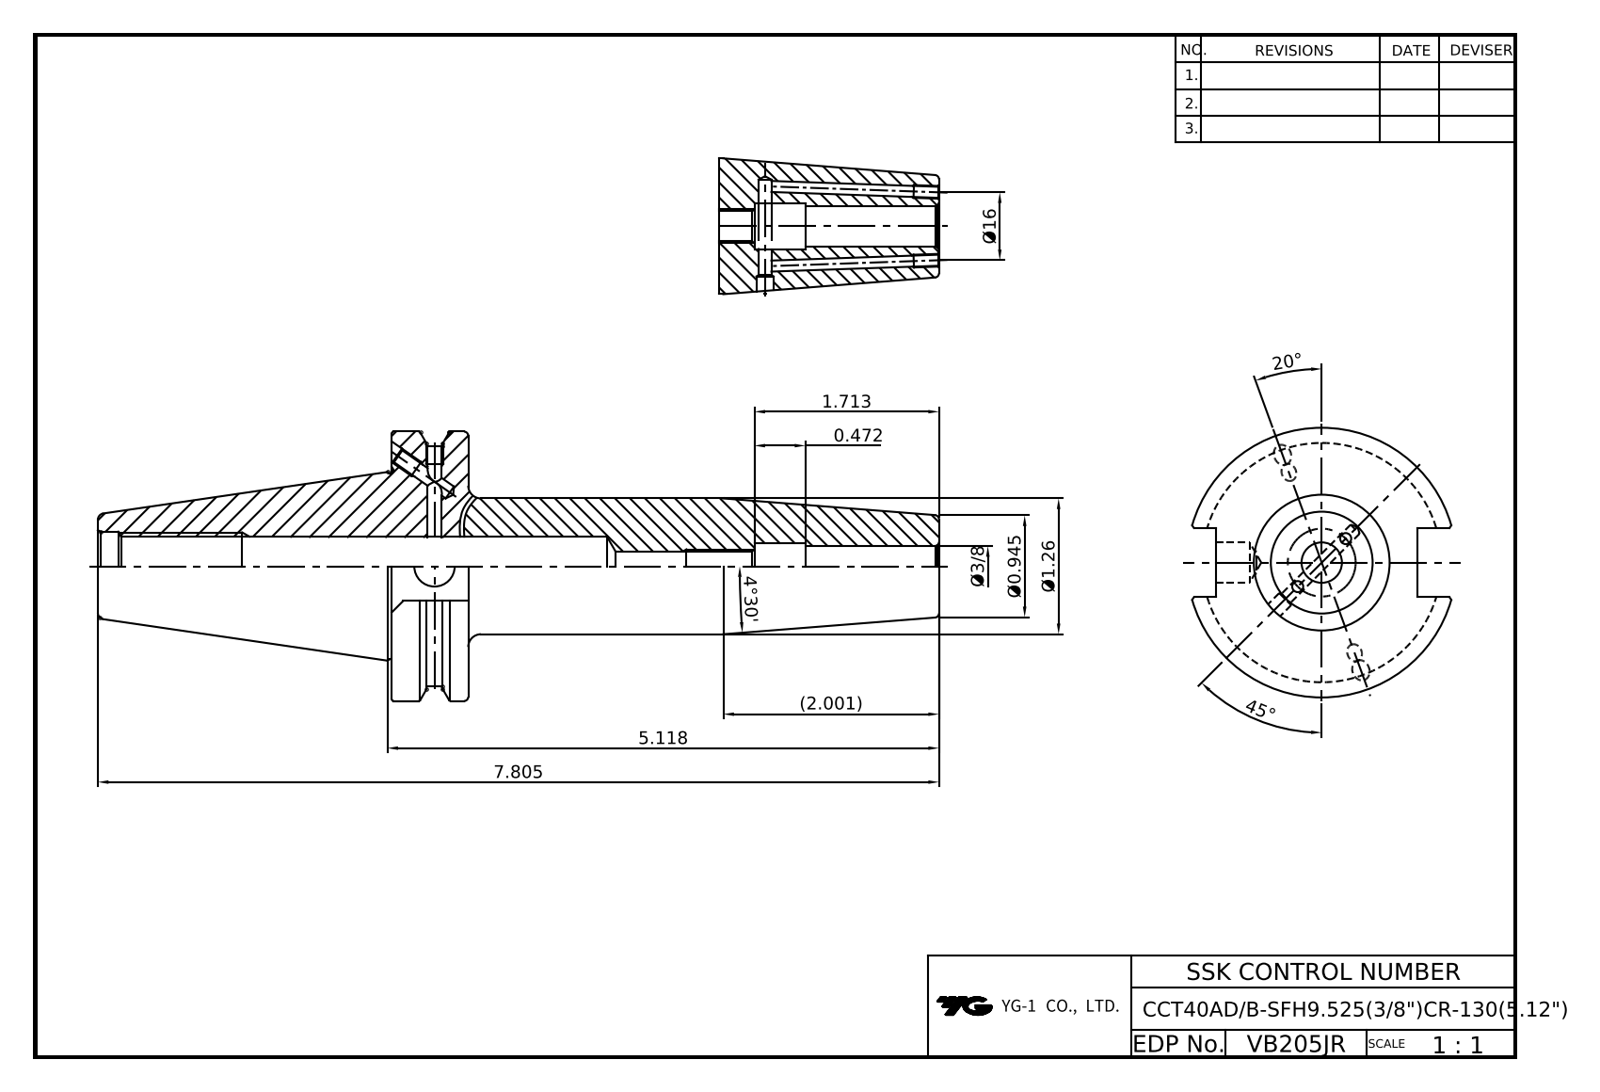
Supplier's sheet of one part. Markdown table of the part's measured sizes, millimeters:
| quantity | value |
| --- | --- |
| part name | LO-CCT40ADB-SFH9.525CR-130 |
| STEP written by | Autodesk Inventor 2026 (AUTOMOTIVE_DESIGN) |
| units | millimeters |
| bodies | 1 solid, 91 faces (38 planar, 30 cylindrical, 23 other) |
| overall size | 198.25 × 63.5 × 61.09 |
| volume | 173 729 mm³ |
| surface area | 35 338 mm² |
| round holes (diameter × count) | 3.24 × 4, 2.46 × 2, 4 × 2, 4.2 × 2, 9.53 × 2, 6.92 × 1, 10.73 × 1, 13.39 × 1, 16.3 × 1 |
| round bosses / shafts (diameter × count) | 63.5 × 1, 43.8 × 1, 32 × 1 |
| partial cylindrical surfaces (radius × count) | 28.15 × 1 |
| main face-to-face distances | 18.05, 129, 110.95, 47.6, 16.38, 69.25, 87.3, 198.25, 81.34, 12.09 |
